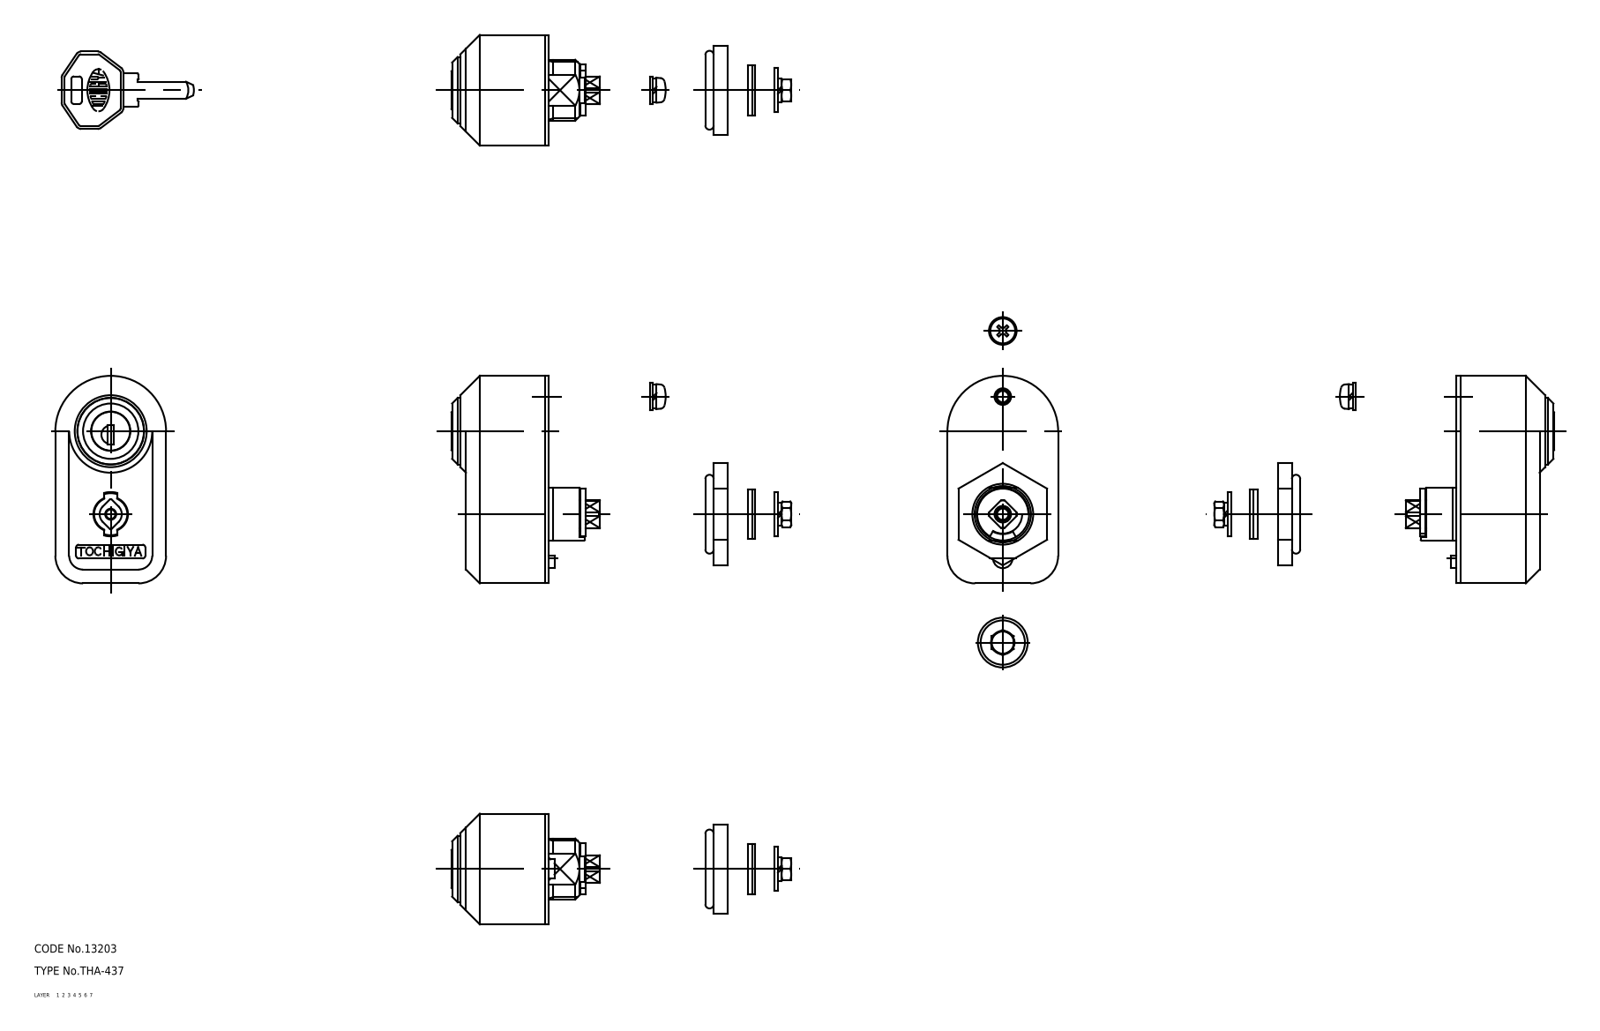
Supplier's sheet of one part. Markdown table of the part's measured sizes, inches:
| quantity | value |
| --- | --- |
| part name | washer_C; washer_B; screw; packing (+6 more) |
| STEP written by | CADfix (AUTOMOTIVE_DESIGN) |
| units | inches |
| bodies | 10 solids, 345 faces (0 planar, 0 cylindrical, 345 other) |
| overall size | 5.926 × 2.953 × 1.575 |
| volume | 5.627 in³ |
| surface area | 42.88 in² |
